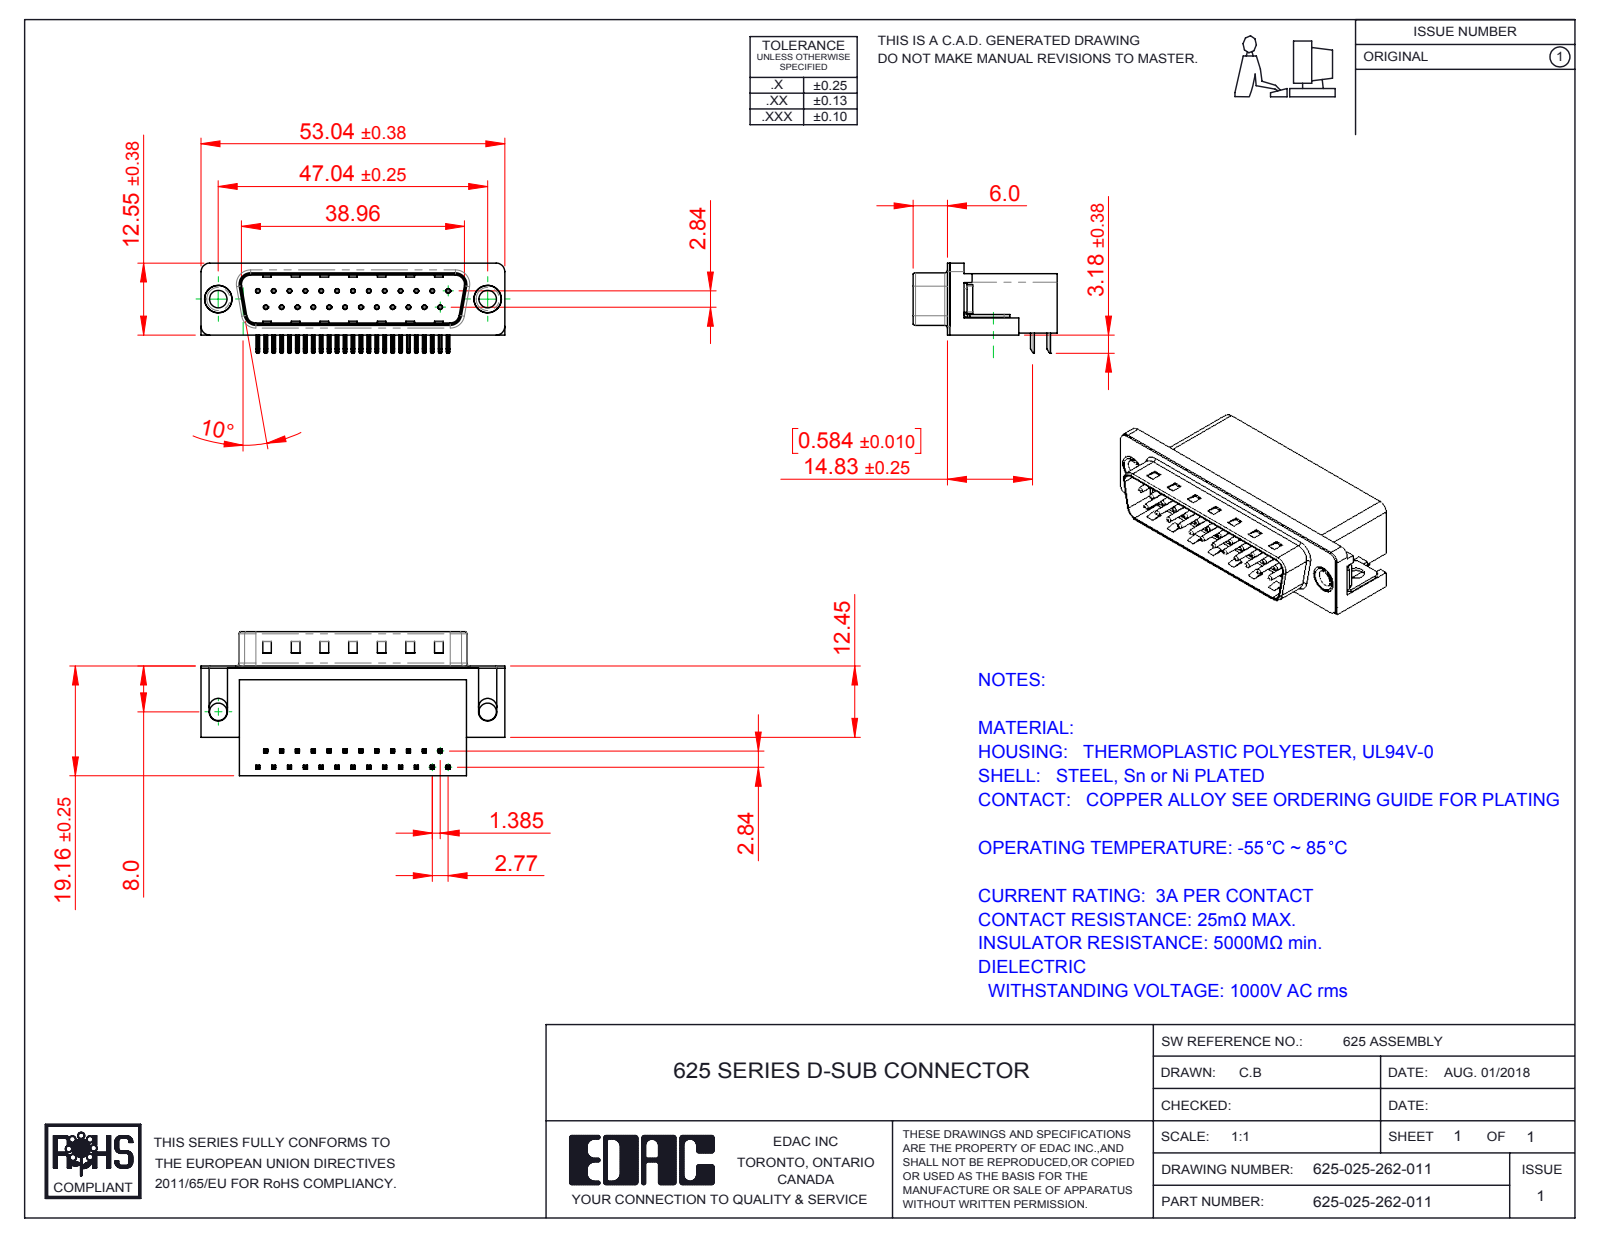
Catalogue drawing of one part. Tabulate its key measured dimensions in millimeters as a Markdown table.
| quantity | value |
| --- | --- |
| part name | 625 Thru Hole Rivet; 625-025-262-011; 625 Contact Bottom; 625 Thru Hole Board Mount (+3 more) |
| STEP written by | SolidWorks 2016 (CONFIG_CONTROL_DESIGN) |
| units | millimeters |
| bodies | 31 solids, 2225 faces (1405 planar, 643 cylindrical, 177 other) |
| overall size | 53.04 × 25.16 × 15.73 |
| volume | 9 150 mm³ |
| surface area | 8 825 mm² |
| round holes (diameter × count) | 0.35 × 25, 0.8 × 25, 3.05 × 4, 4 × 2, 4.8 × 2, 5 × 2 |
| round bosses / shafts (diameter × count) | 0.75 × 25, 4.9 × 2, 4.75 × 2, 3.85 × 2 |
| partial cylindrical surfaces (radius × count) | 0.25 × 108, 0.12 × 50, 1 × 16, 0.5 × 9, 1.6 × 8, 1.5 × 7, 0.9 × 4, 2 × 4 |
| main face-to-face distances | 0.4, 10.35, 18.76, 2.1, 8.76, 10.46, 10.86, 1.7, 19.16, 10.11 |
| hole center spacings | 3.16, 2.77, 11.08, 5.54, 8.31, 5.03, 13.85, 7.48 |
